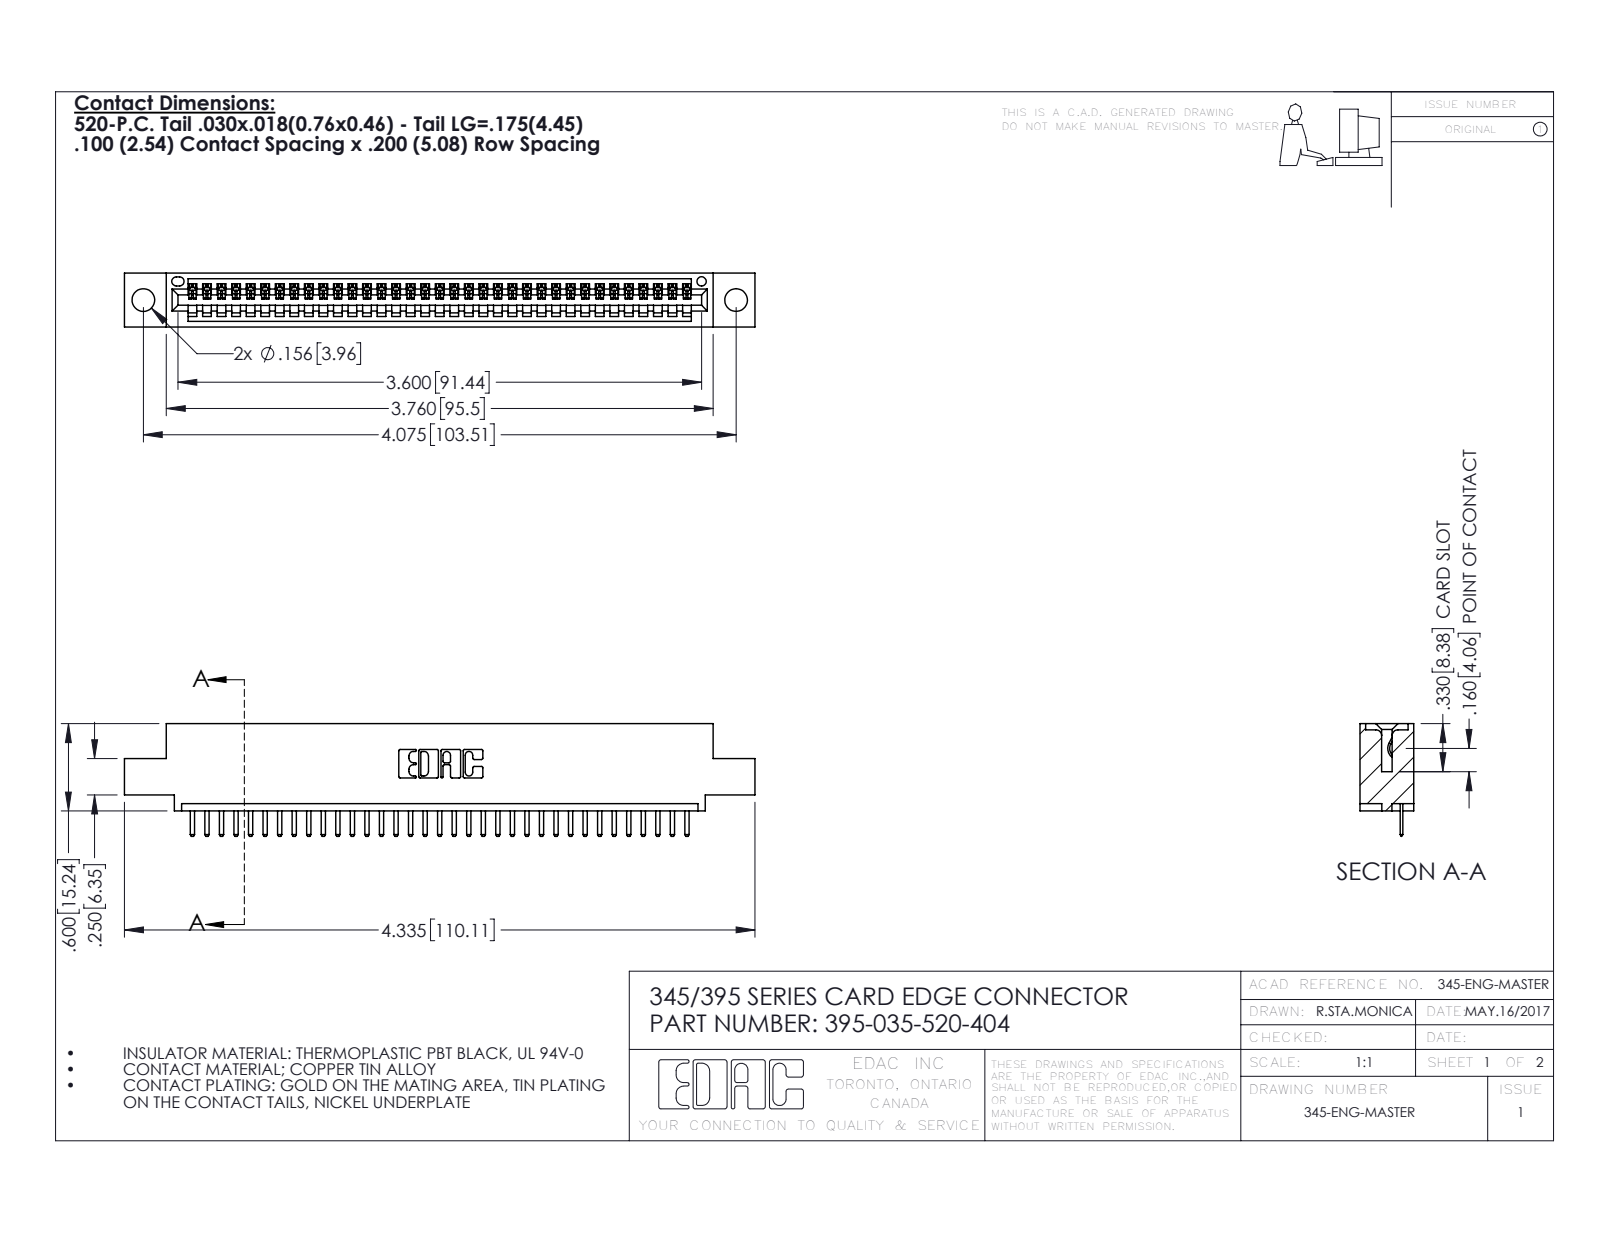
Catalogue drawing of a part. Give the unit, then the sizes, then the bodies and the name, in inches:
Units: inches
Overall size (bounding box): 4.335 × 0.775 × 0.37
Round holes (diameter × count): ⌀0.156 ×2, ⌀0.064 ×1
Partial cylindrical surfaces — rounded edges, fillets, slot ends (radius × count): R0.01 ×72, R0.006 ×70, R0.01 ×22, R0.007 ×6, R0.031 ×6, R0.026 ×3, R0.031 ×2, R0.04 ×2
Main face-to-face distances: 0.298, 0.072, 0.37, 0.2, 0.098, 0.272, 0.025, 0.225, 0.072, 0.149
Hole centre spacings: 0.27, 3.839, 4.075
Volume: 0.619 in³ · Surface area: 20.06 in²
Bodies: 36 solids, 2300 faces (1554 planar, 746 cylindrical, 0 other)
Part name (STEP PRODUCT): 345 Part_0.110 Offset - 0.156 Dia-TH; 395-035-520-404; 345-292-001_345-293-120
STEP written by: SolidWorks 2016 (CONFIG_CONTROL_DESIGN)
